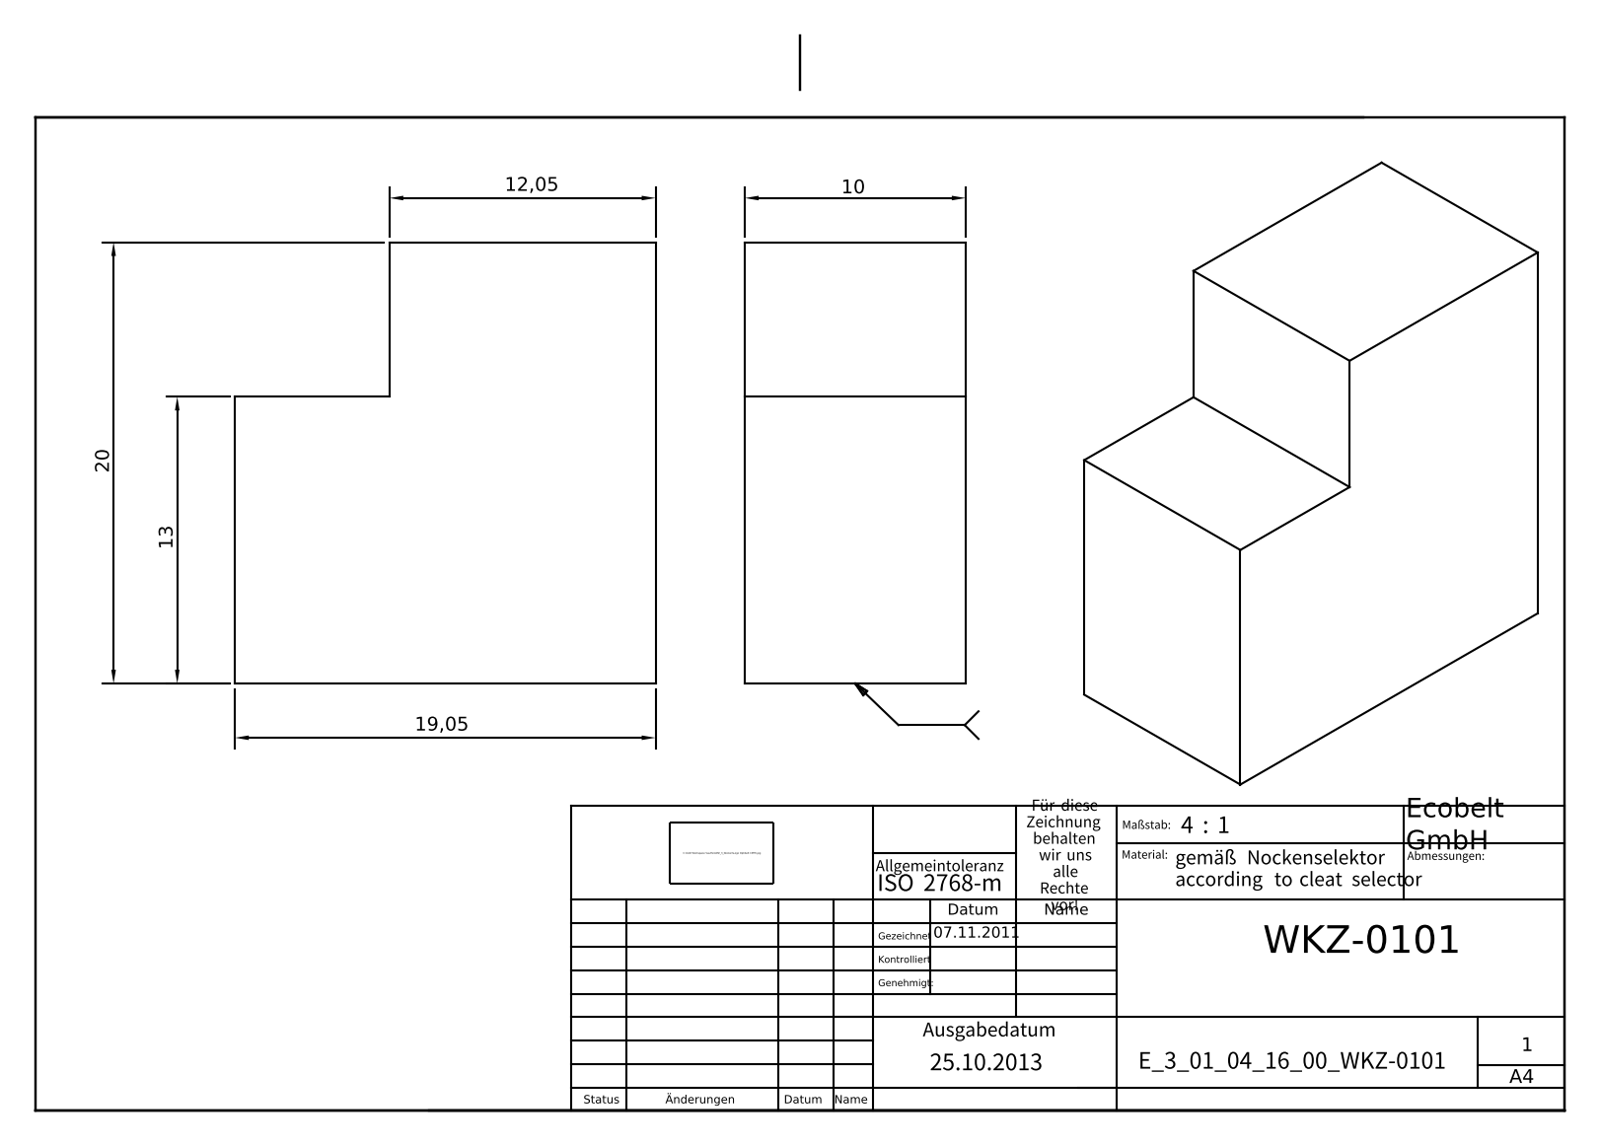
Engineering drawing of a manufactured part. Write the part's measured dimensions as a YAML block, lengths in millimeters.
part_name: "E_3_01_04_16_00_WKZ-0101"
step_written_by: "Autodesk Inventor 2025 (AUTOMOTIVE_DESIGN)"
units: millimeters
bodies: {solids: 1, faces: 8, planar: 8, cylindrical: 0, other: 0}
overall_size: [20, 19.05, 10]
volume: 3320
surface_area: 1445
face_to_face_distances: [10, 7, 19.05, 20, 12.05, 13]
